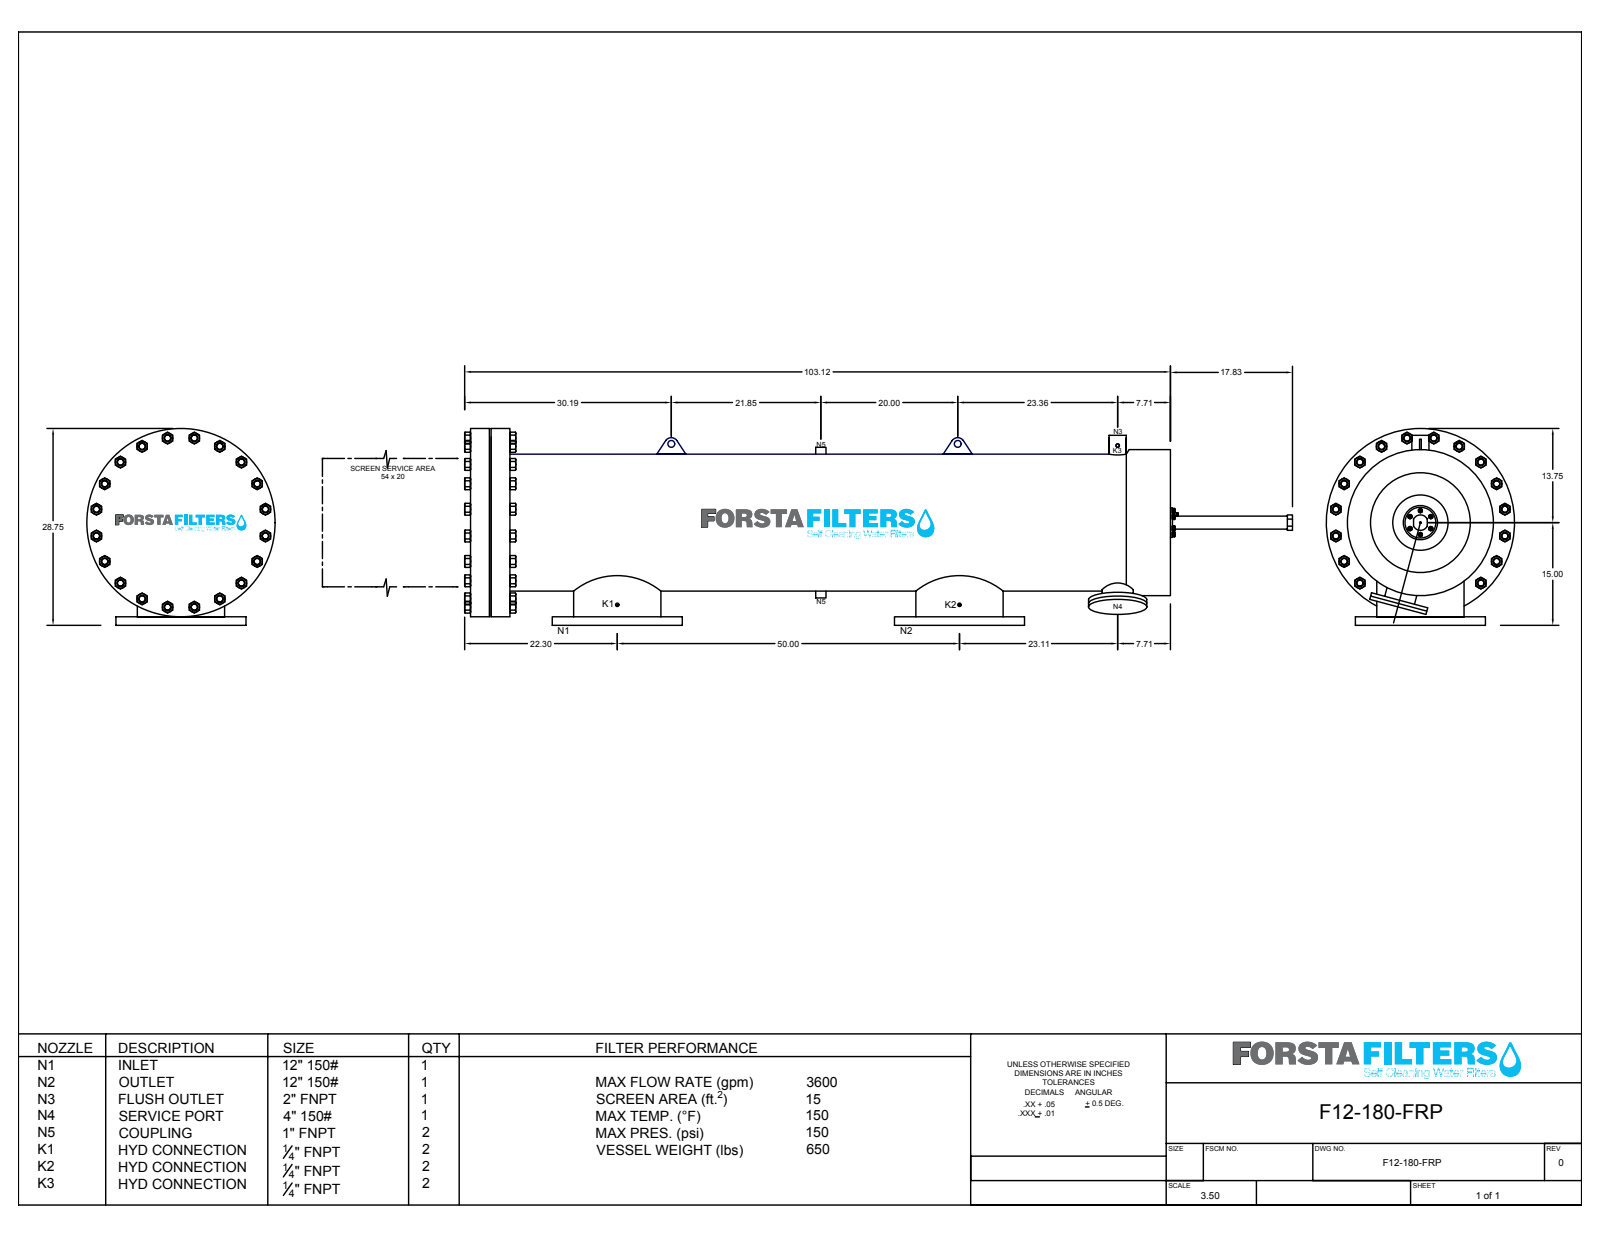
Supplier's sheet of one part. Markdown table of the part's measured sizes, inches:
| quantity | value |
| --- | --- |
| part name | F12-FRP-180 |
| STEP written by | SolidWorks 2018 (CONFIG_CONTROL_DESIGN) |
| units | inches |
| bodies | 23 solids, 787 faces (372 planar, 402 cylindrical, 13 other) |
| overall size | 116.454 × 28.749 × 27.498 |
| volume | 4 400 in³ |
| surface area | 18 693 in² |
| round holes (diameter × count) | 1 × 43, 0.75 × 16, 0.38 × 6, 0.25 × 3, 4 × 2, 12 × 2, 0.246 × 1, 1.394 × 1, 2 × 1, 20.931 × 1 |
| round bosses / shafts (diameter × count) | 0.375 × 5, 19 × 2, 12.394 × 2, 9 × 2, 4.394 × 2, 0.644 × 2, 27.498 × 1, 21.325 × 1 |
| partial cylindrical surfaces (radius × count) | 1 × 2 |
| main face-to-face distances | 2.75, 3, 0.25, 97.951, 95.201, 94.951, 97.754, 95.004, 94.754, 0.197 |
| hole center spacings | 8.5, 14.722, 4.4, 5.303, 12.5, 16.421, 17.678, 20.787 |
